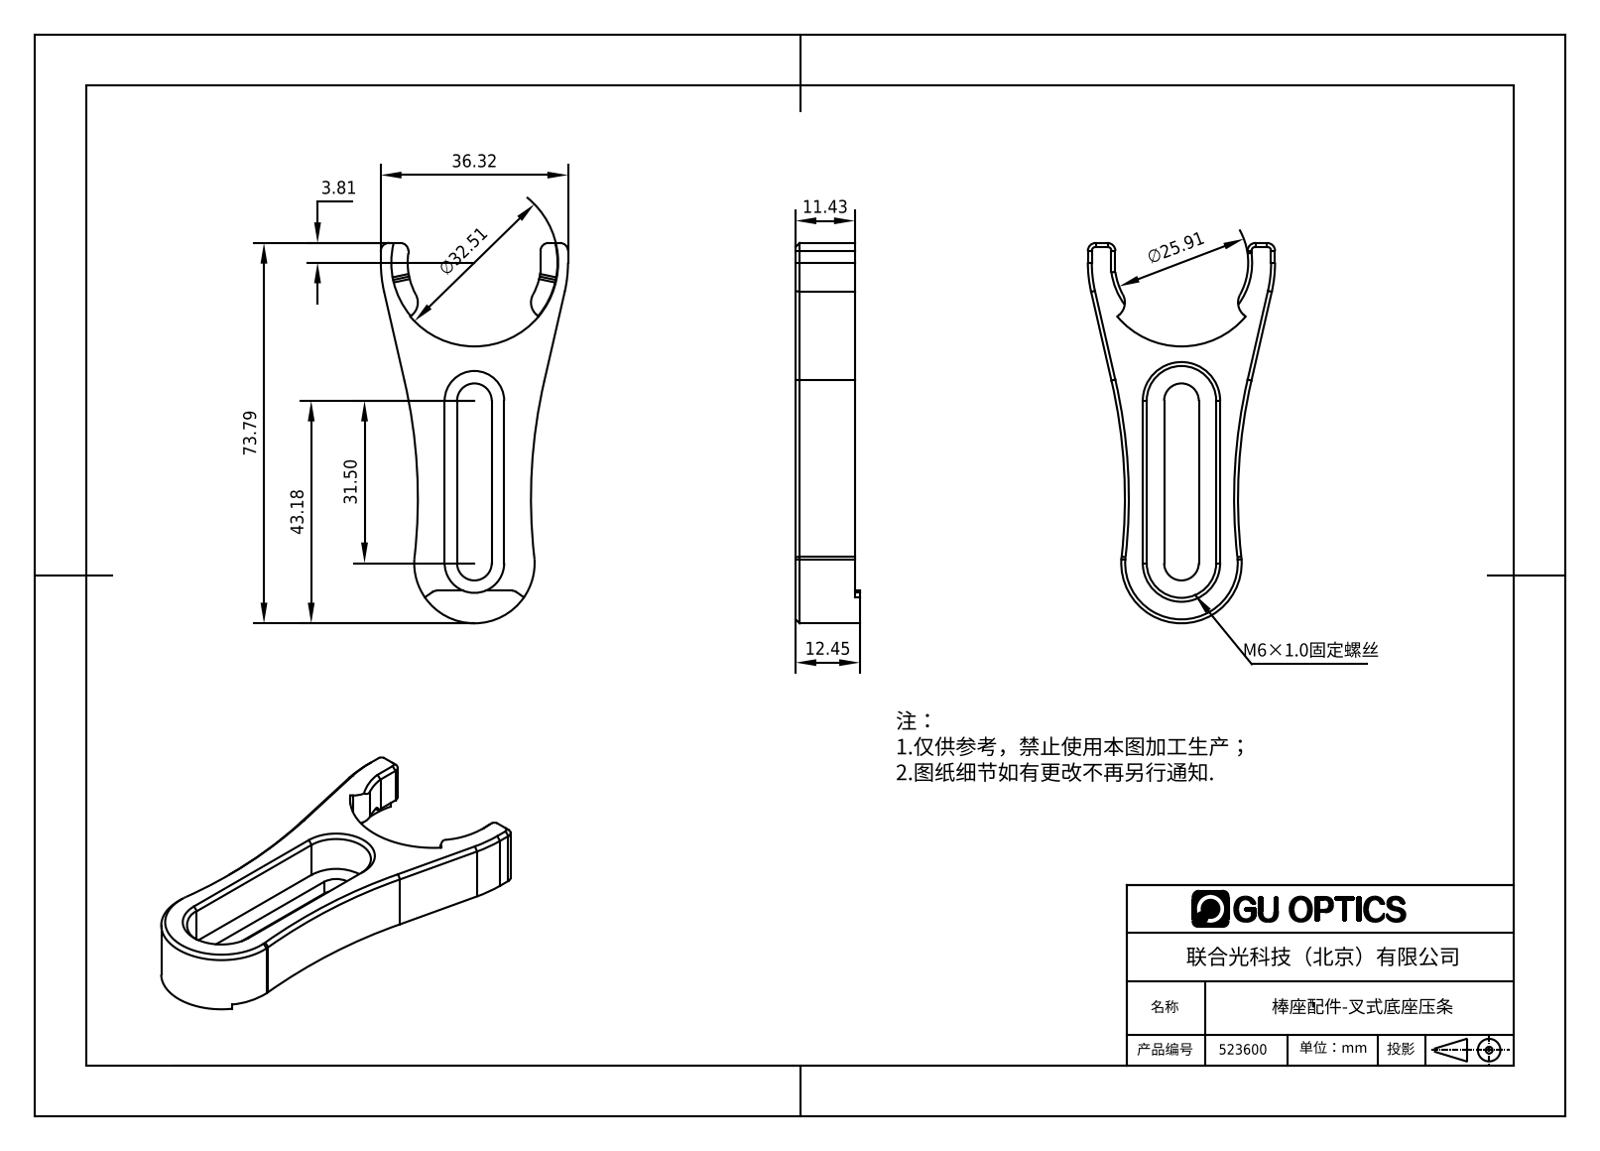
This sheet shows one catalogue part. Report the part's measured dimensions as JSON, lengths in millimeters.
{"part_name": "523600", "step_written_by": "SolidWorks 2016 (AUTOMOTIVE_DESIGN)", "units": "millimeters", "bodies": {"solids": 1, "faces": 89, "planar": 39, "cylindrical": 34, "other": 16}, "overall_size": [73.8, 36.3, 12.4], "volume_mm3": 10900, "surface_area_mm2": 6088, "partial_cylinders_radius": [[0.5, 4], [1.5, 4], [1.6, 2], [3.2, 2], [3.4, 2], [6.5, 2], [6.8, 2], [25.4, 2]], "face_to_face_distances": [11.4, 3.6, 7.9, 13.5, 0.8, 2.8, 10.7, 3.4, 10.1, 1]}
